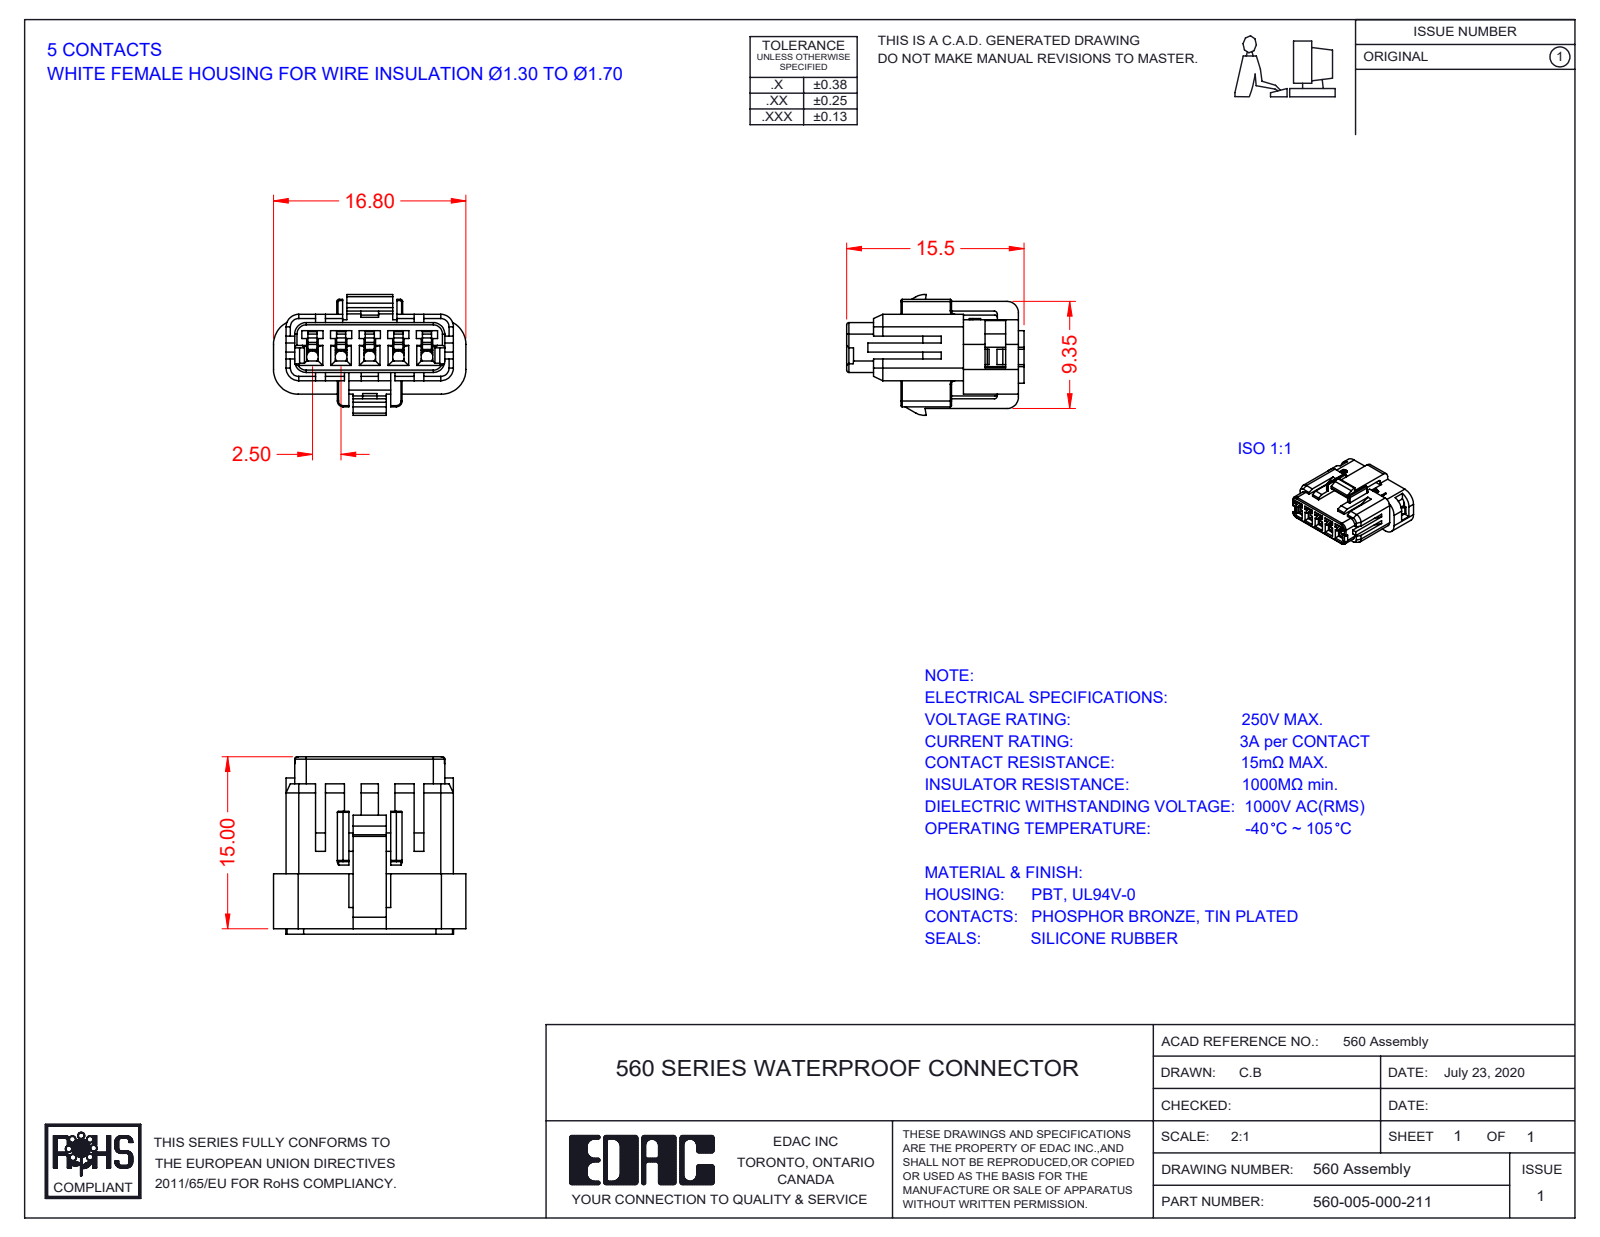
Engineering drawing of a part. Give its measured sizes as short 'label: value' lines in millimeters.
name: FEMALE_HOUSING_5POS_WHITE; REAR-INSULATOR-5POS-1; REAR-GASKET-5POS_ORANGE; 560-005-000-211
written by: SolidWorks 2020 (CONFIG_CONTROL_DESIGN)
unit: mm
bodies: 3 solids, 936 faces (560 planar, 172 cylindrical, 204 other)
size: 16.8 × 15.48 × 10.55
volume: 1 037 mm³; area: 2 491 mm²
holes: 5× ⌀1.5
rounds: 13× R0.1, 12× R1.2, 10× R0.2, 10× R1, 8× R0.15, 6× R1.5, 4× R0.3, 4× R0.8
face distances: 3.8, 0.7, 5.65, 1.6, 0.8, 0.9, 3.1, 0.95, 3.9, 0.85
hole spacings: 2.5, 5, 7.5, 10
